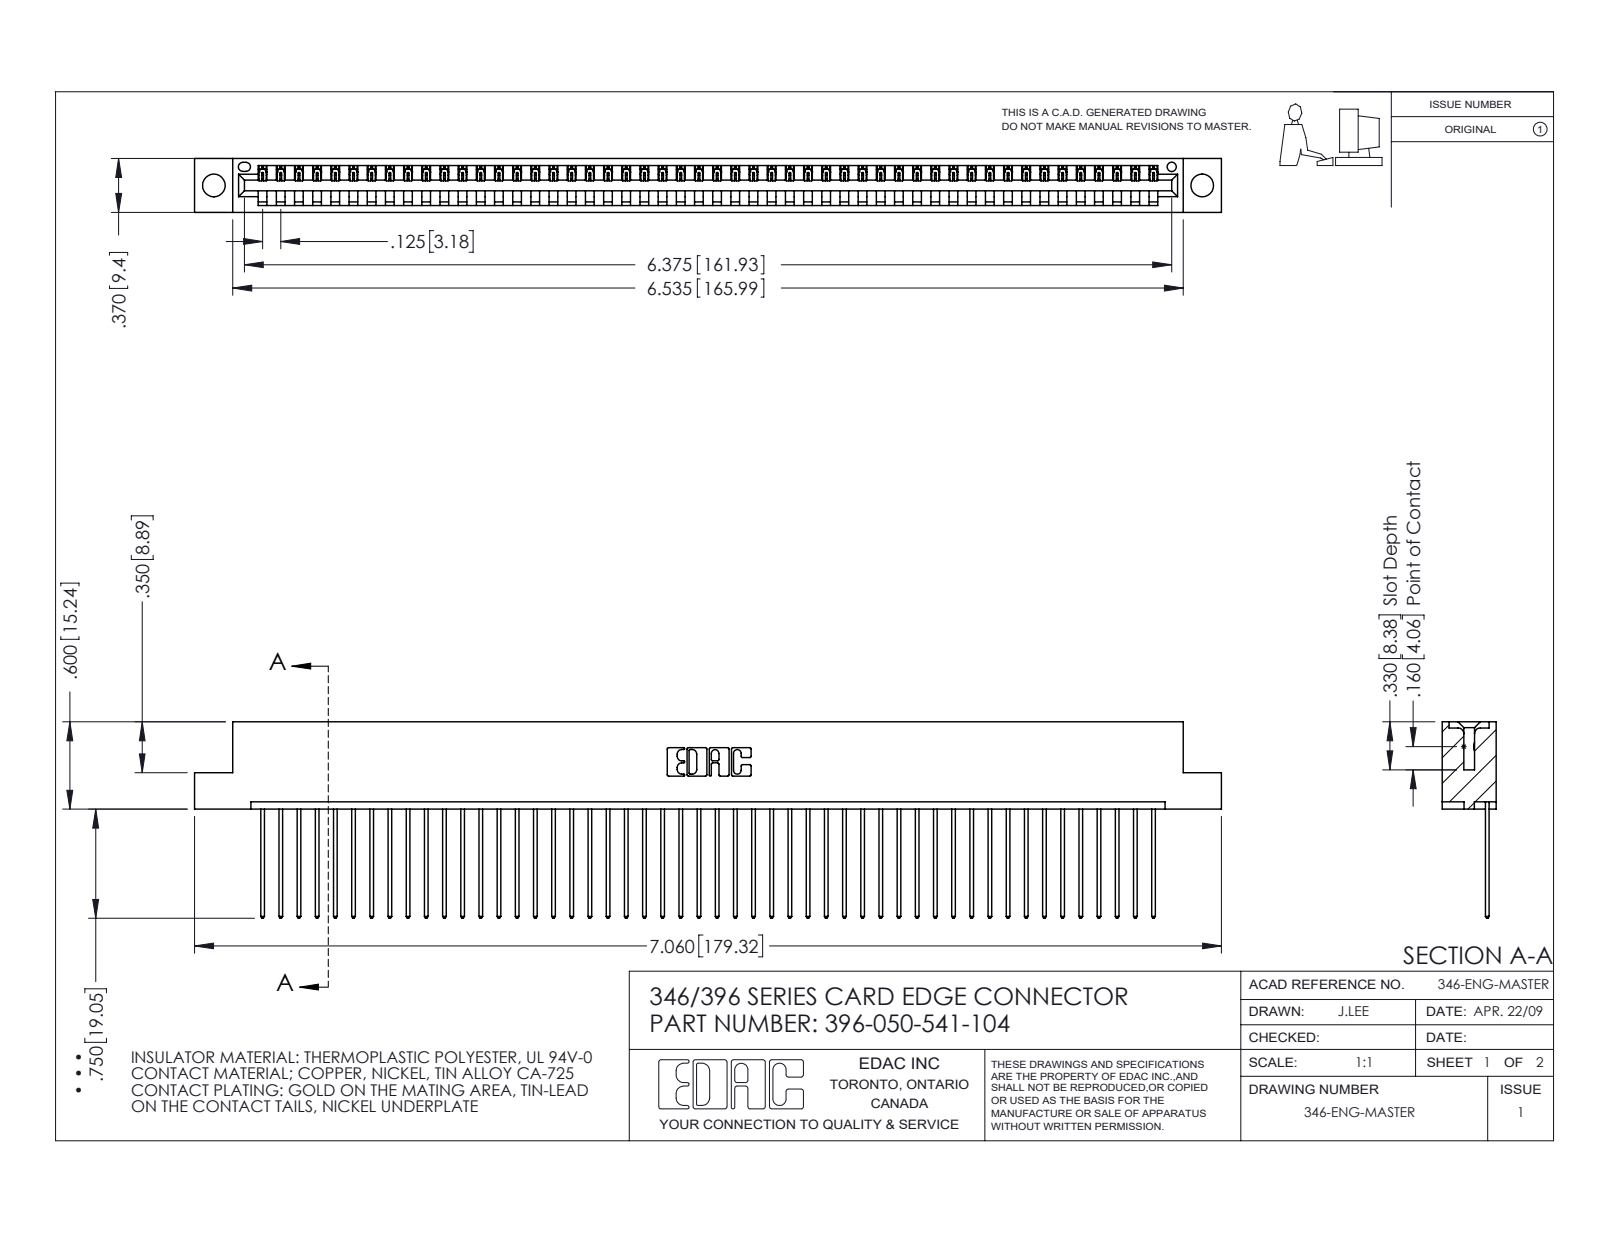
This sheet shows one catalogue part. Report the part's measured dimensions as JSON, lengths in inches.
{"part_name": "345-292-001_345-293-141; 346 Part_Flush Mounting Lugs - 0.156 Dia-TH; 396-050-541-104", "step_written_by": "SolidWorks 2016 (CONFIG_CONTROL_DESIGN)", "units": "inches", "bodies": {"solids": 51, "faces": 3022, "planar": 2076, "cylindrical": 946, "other": 0}, "overall_size": [7.06, 1.35, 0.37], "volume_in3": 1.056, "surface_area_in2": 34.87, "round_holes": [[0.156, 2], [0.064, 1]], "partial_cylinders_radius": [[0.006, 100], [0.01, 100], [0.01, 22], [0.007, 6], [0.031, 6], [0.026, 3], [0.031, 2], [0.04, 2]], "face_to_face_distances": [0.048, 0.322, 0.37, 0.25, 0.072, 0.298, 0.025, 0.148, 0.222, 0.1], "hole_center_spacings": [0.246, 6.586, 6.795]}
